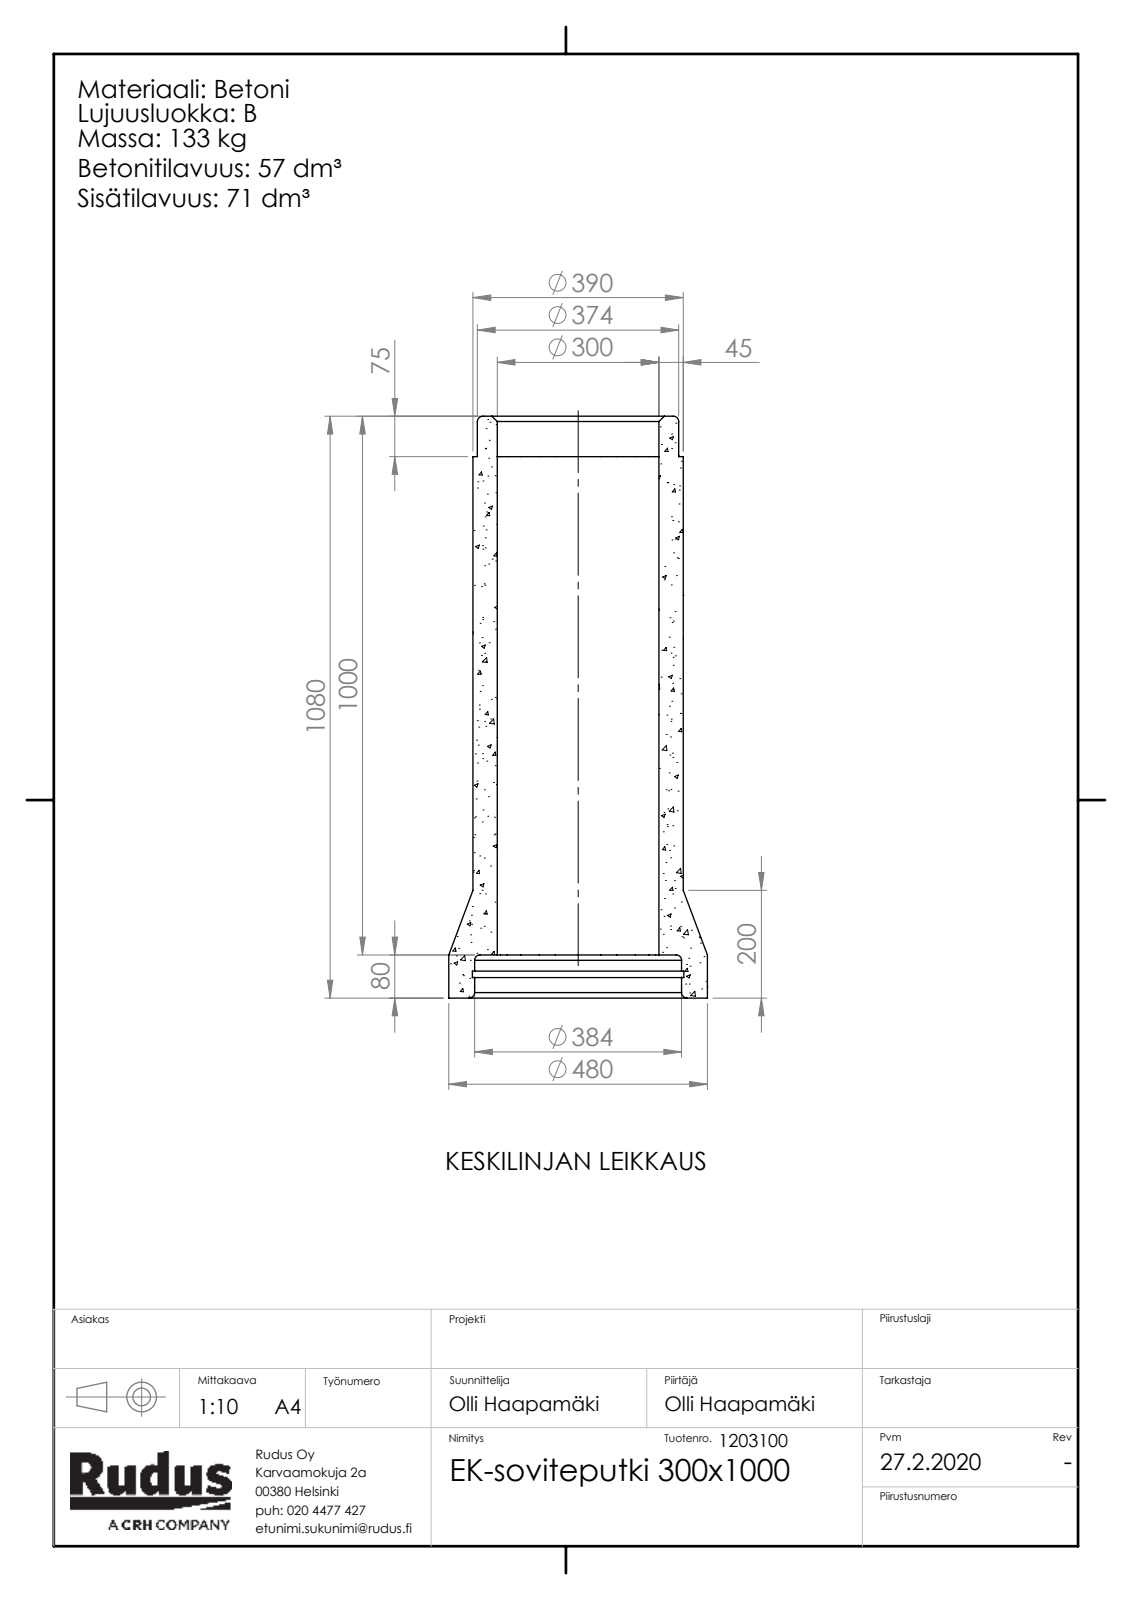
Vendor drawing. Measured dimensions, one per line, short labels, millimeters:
name: Rudus 1203100 EK-soviteputki 300x1000; EK-osa-putkirunko
written by: SolidWorks 2019 (CONFIG_CONTROL_DESIGN)
unit: mm
bodies: 1 solid, 109 faces (15 planar, 12 cylindrical, 82 other)
size: 1080 × 480 × 480
volume: 56 620 000 mm³; area: 2 562 000 mm²
holes: 1× ⌀300, 1× ⌀384, 1× ⌀392
bosses: 1× ⌀480, 1× ⌀373.6
face distances: 80, 1080, 1000, 1005, 925, 75, 38, 42, 967, 1042
